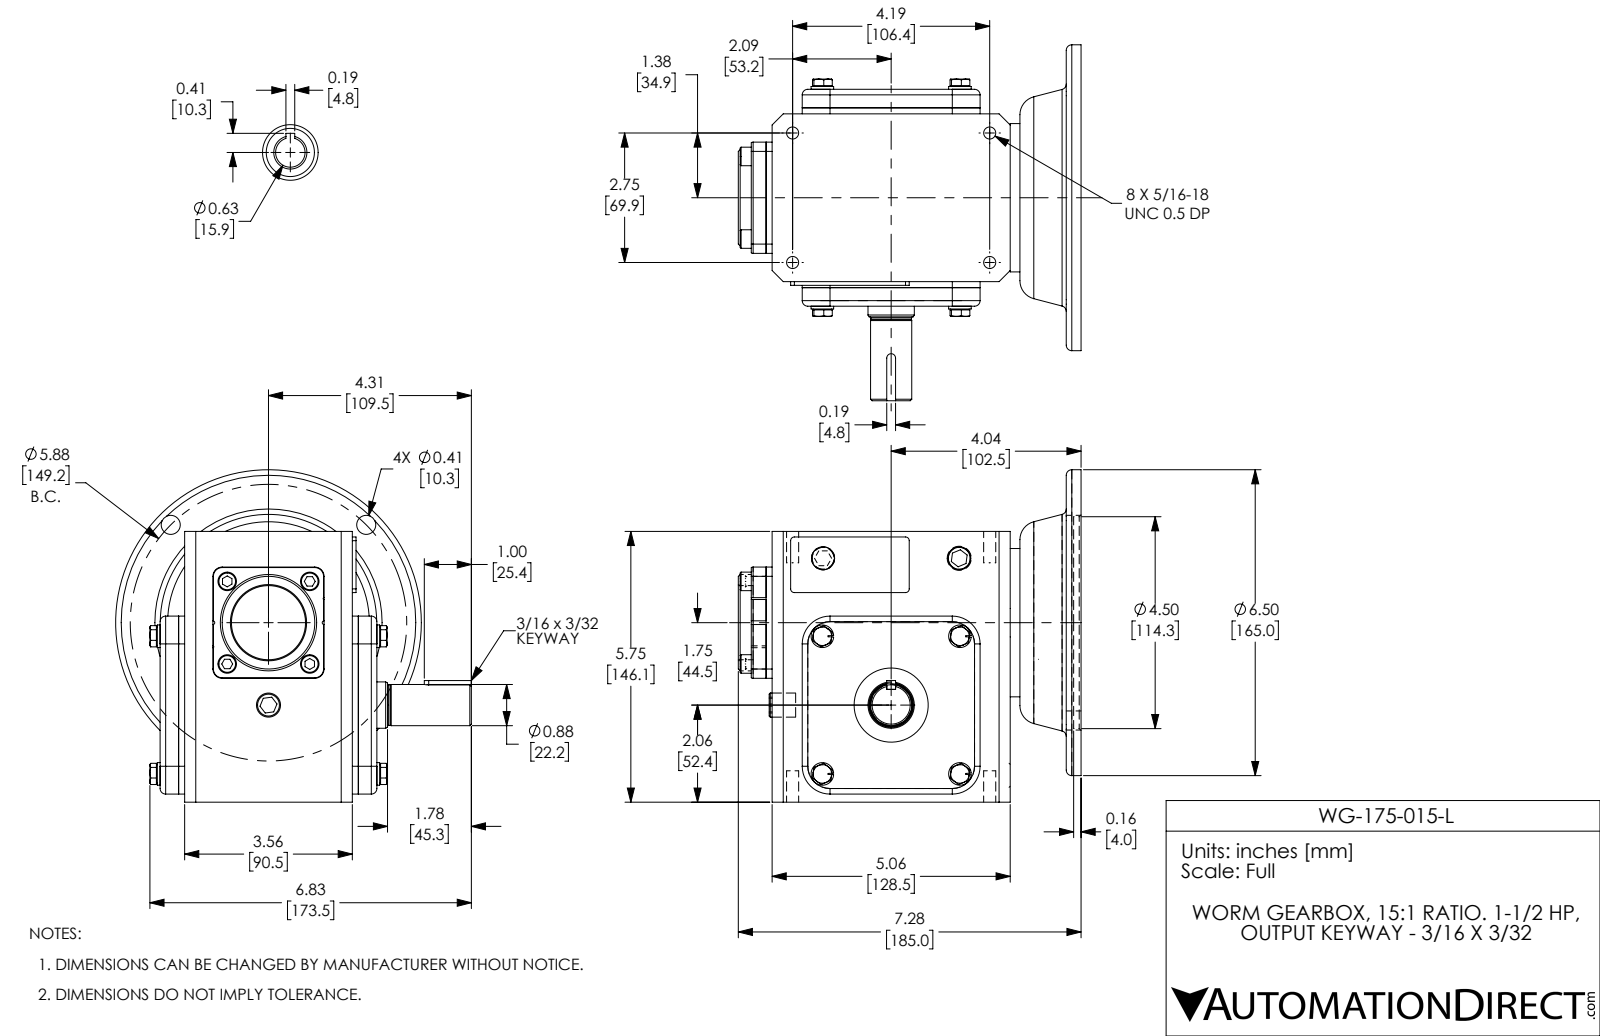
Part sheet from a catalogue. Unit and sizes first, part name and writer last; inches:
Units: inches
Overall size (bounding box): 7.559 × 7.283 × 7.06
Round holes (diameter × count): ⌀0.257 ×4, ⌀0.406 ×4, ⌀0.512 ×1, ⌀0.625 ×1, ⌀0.984 ×1, ⌀1.181 ×1, ⌀1.457 ×1, ⌀1.575 ×1, ⌀3.543 ×1, ⌀4.5 ×1
Round bosses / shafts (diameter × count): ⌀0.394 ×8, ⌀0.48 ×4, ⌀0.512 ×2, ⌀6.496 ×1, ⌀3.15 ×1, ⌀2.047 ×1, ⌀1.575 ×1, ⌀0.875 ×1
Partial cylindrical surfaces — rounded edges, fillets, slot ends (radius × count): R0.079 ×8, R0.118 ×8, R0.197 ×4, R0.591 ×4, R0.02 ×2, R0.039 ×2, R0.094 ×1
Main face-to-face distances: 0.128, 3.819, 4.213, 0.394, 0.522, 3.691, 4.085, 0.315, 5.75, 6.693
Hole centre spacings: 2.937, 4.154, 2.103, 2.75, 4.188, 4.354, 5.01, 5.875
Volume: 131.9 in³ · Surface area: 366.4 in²
Bodies: 43 solids, 613 faces (312 planar, 172 cylindrical, 129 other)
Part name (STEP PRODUCT): WG-175-015-L
STEP written by: SolidWorks 2017 (AUTOMOTIVE_DESIGN)
